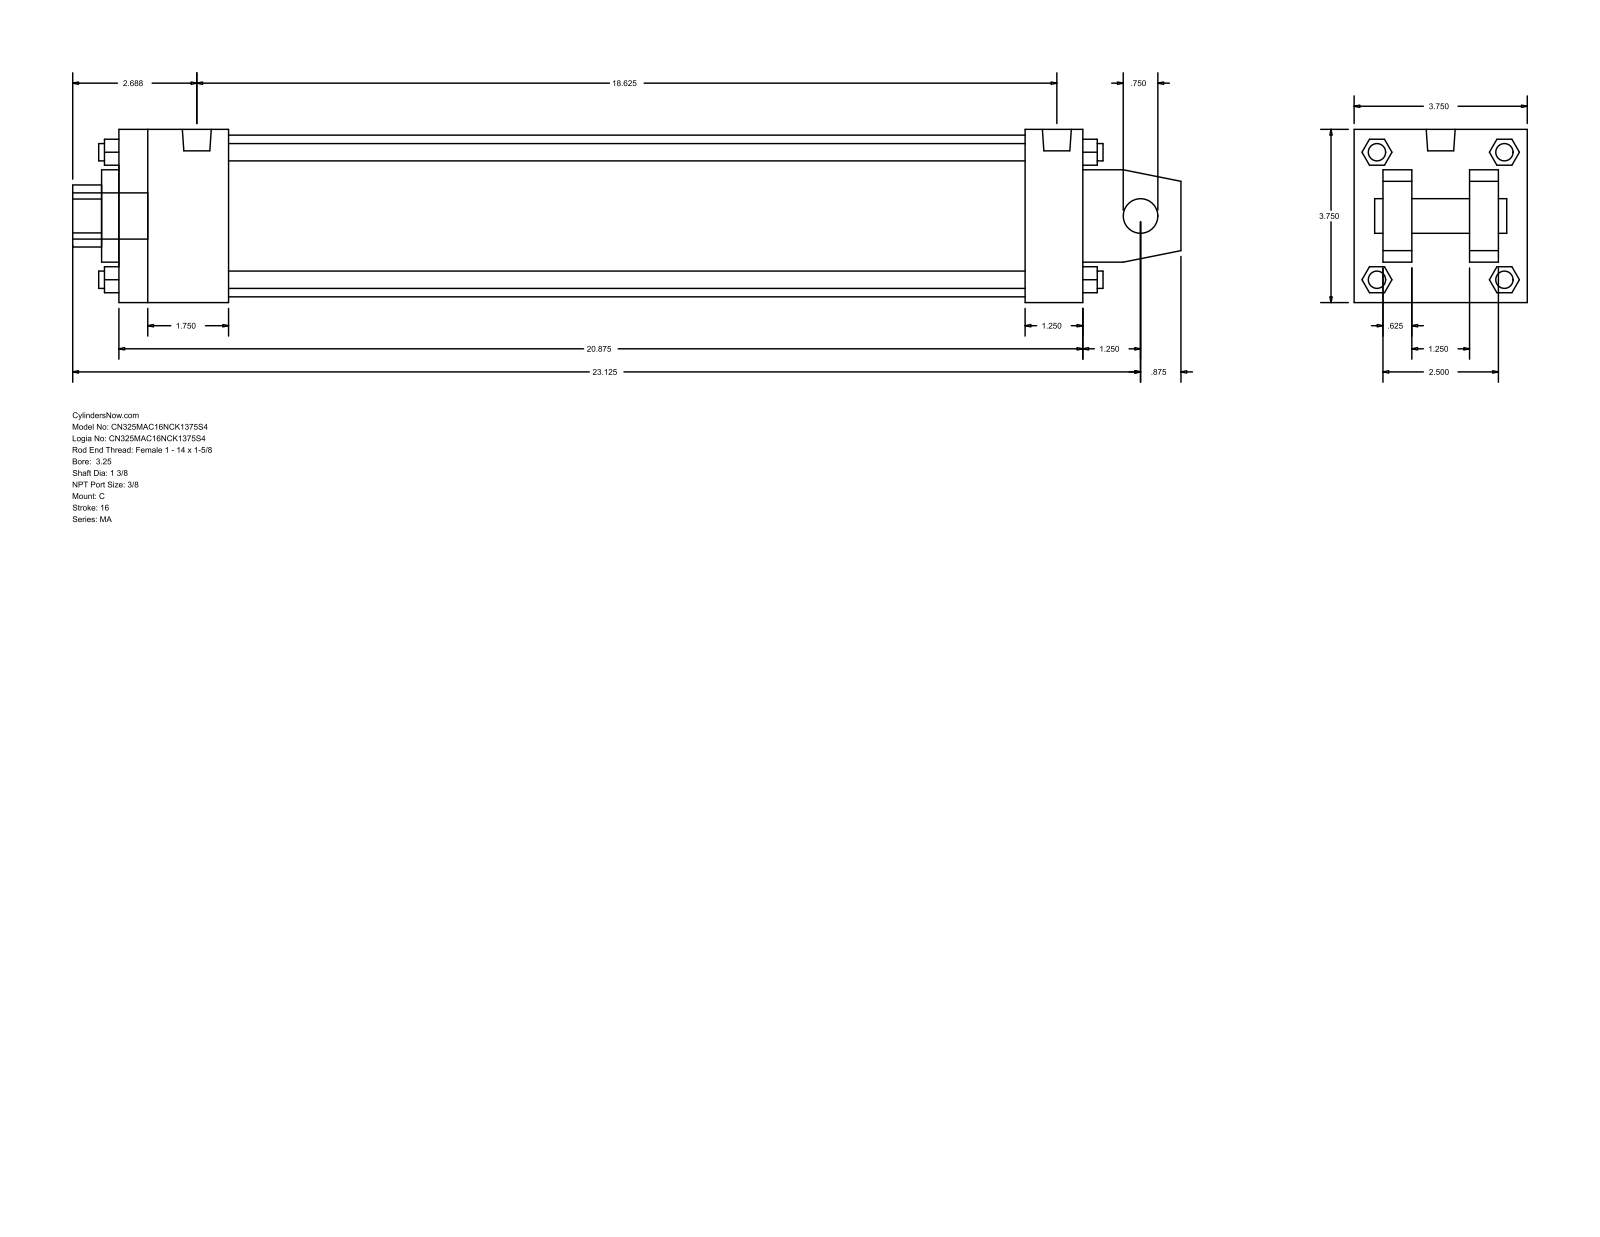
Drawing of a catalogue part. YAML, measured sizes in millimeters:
part_name: "MA_C__0325_1.375"
step_written_by: "GSSL Pune (CONFIG_CONTROL_DESIGN)"
units: millimeters
bodies: {solids: 0, faces: 139, planar: 108, cylindrical: 31, other: 0}
overall_size: [609.6, 95.25, 95.25]
round_holes:
  - {diameter: 19.05, count: 1}
  - {diameter: 34.92, count: 1}
  - {diameter: 50.8, count: 1}
  - {diameter: 88.9, count: 1}
round_bosses_or_shafts:
  - {diameter: 11.11, count: 4}
  - {diameter: 9.53, count: 4}
  - {diameter: 15.93, count: 2}
  - {diameter: 25.4, count: 1}
partial_cylinders:
  - {radius: 17.06, count: 1}
face_to_face_distances: [95.24, 15.87, 31.74, 63.5, 530.22, 79.37, 47.63, 498.48, 60.32, 438.16]
